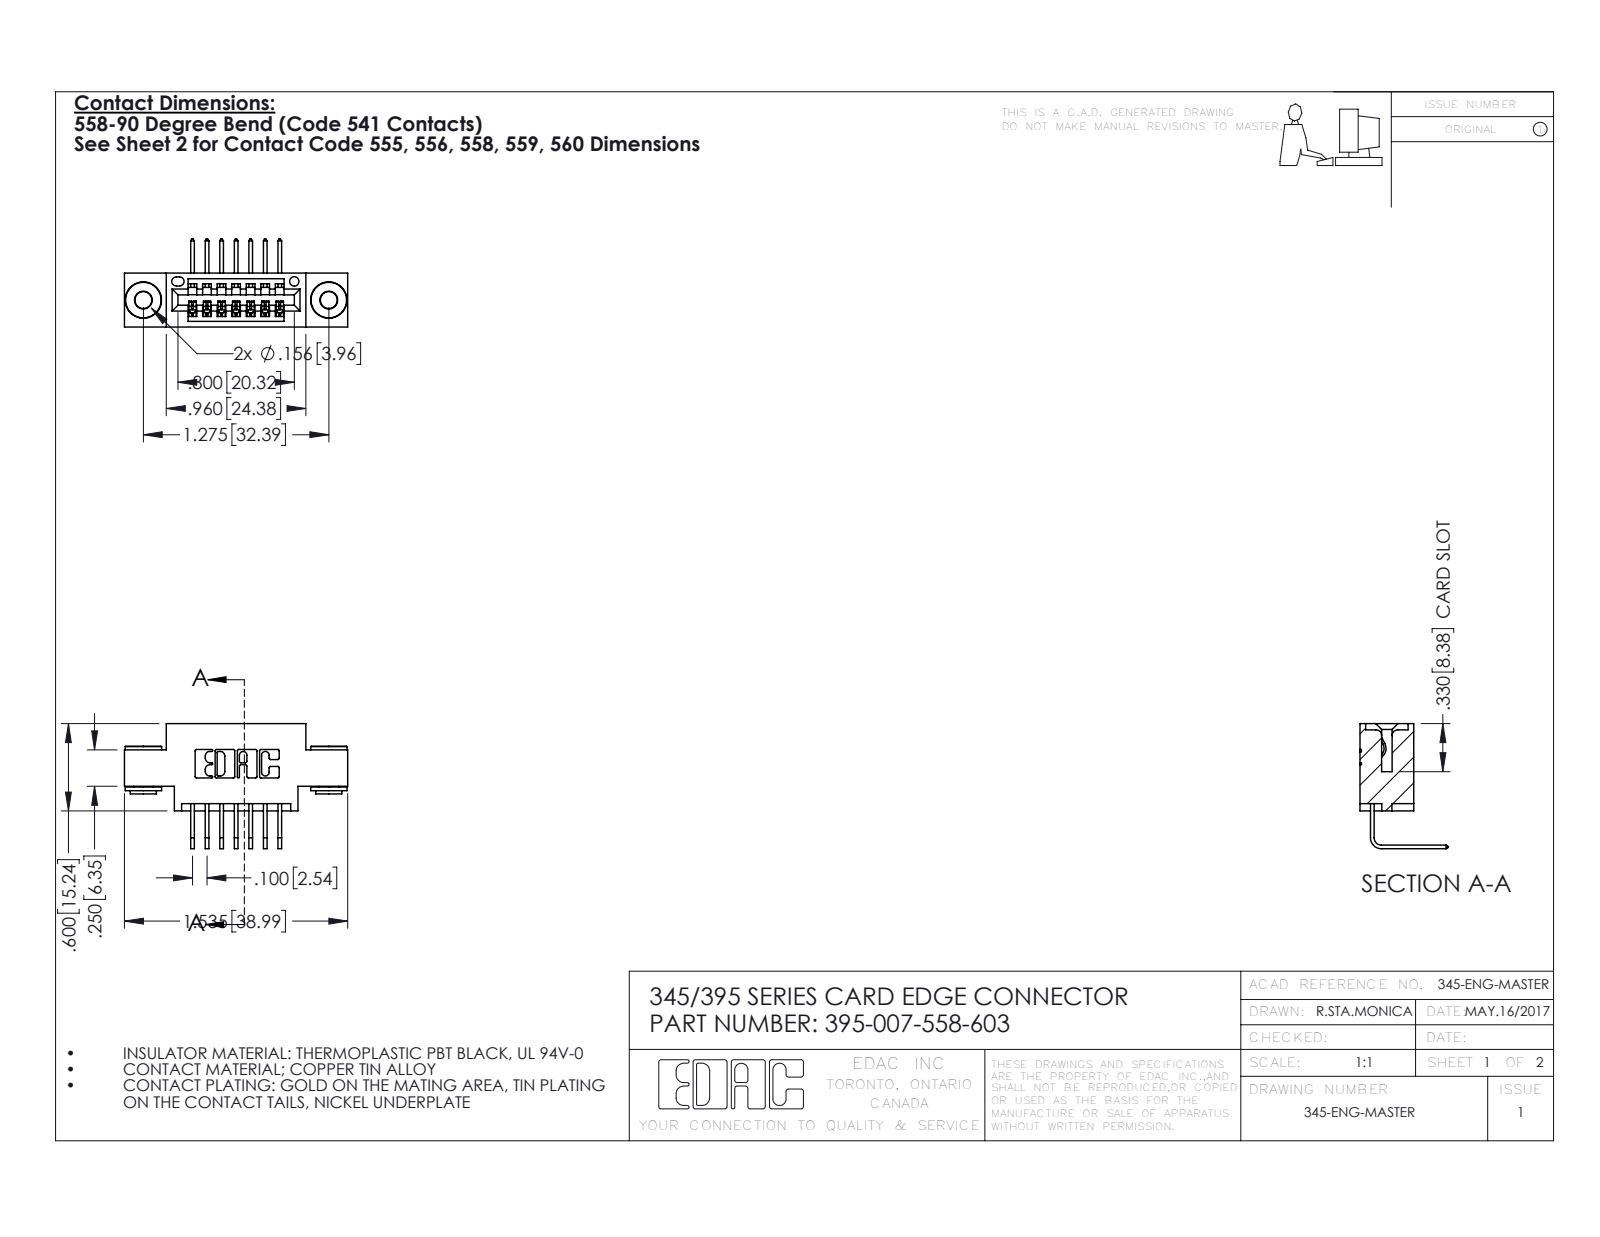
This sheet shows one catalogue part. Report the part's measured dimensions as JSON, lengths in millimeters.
{"part_name": "345 Part_0.170 Offset - 0.156 Dia-TH; 395-007-558-603; 345-292-001_558 Tail - 2; 345-250-002_345-250-002-102", "step_written_by": "SolidWorks 2016 (CONFIG_CONTROL_DESIGN)", "units": "millimeters", "bodies": {"solids": 10, "faces": 588, "planar": 388, "cylindrical": 192, "other": 8}, "overall_size": [39, 21.8, 15.4], "volume_mm3": 3340, "surface_area_mm2": 4449, "round_holes": [[2.9, 2], [4, 2], [1.6, 1]], "round_bosses_or_shafts": [[6.4, 2], [4.6, 2], [3.5, 2]], "partial_cylinders_radius": [[0.3, 22], [0.2, 14], [0.2, 6], [0.8, 6], [0.7, 3], [0.8, 2], [1, 2], [0.4, 1]], "face_to_face_distances": [5.1, 9.4, 2.5, 1.8, 7.6, 7.6, 2.5, 6.9, 0.6, 1.5], "hole_center_spacings": [6.9, 26.5, 32.4]}
